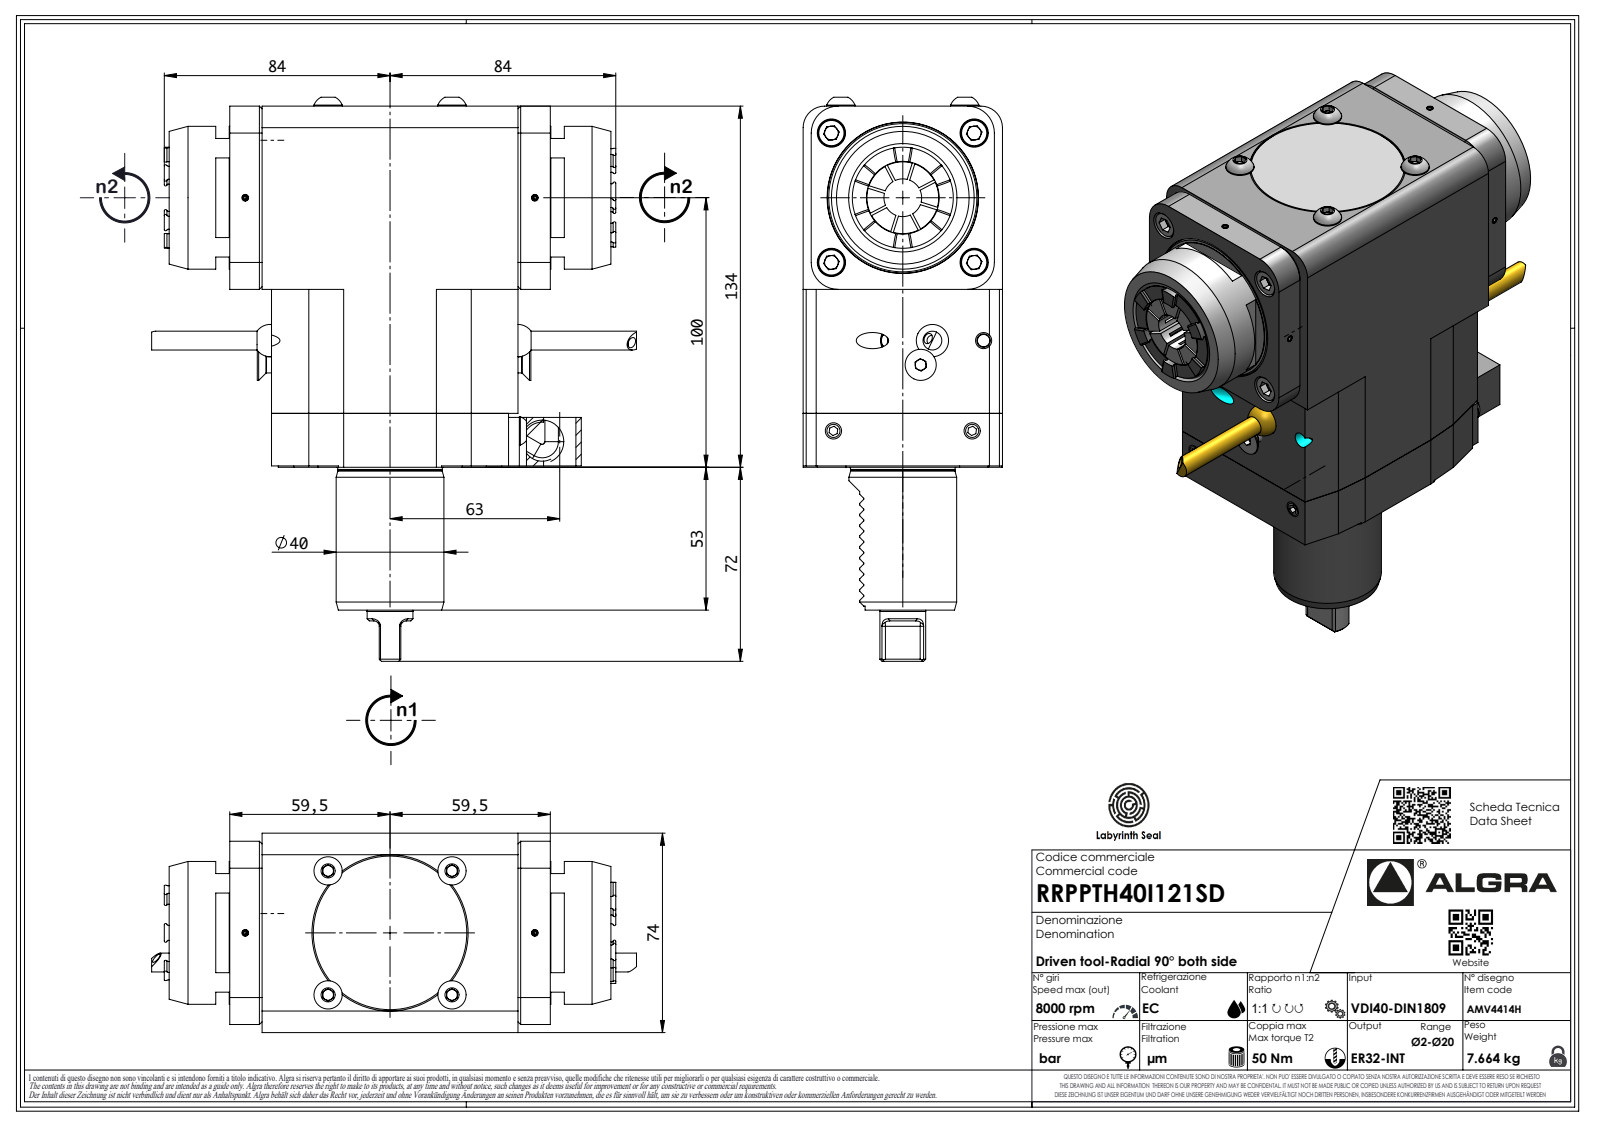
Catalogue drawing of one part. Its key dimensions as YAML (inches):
part_name: "RRPPTH40I121SD"
step_written_by: "SolidWorks 2023 (AUTOMOTIVE_DESIGN)"
units: inches
bodies: {solids: 1, faces: 472, planar: 331, cylindrical: 62, other: 79}
overall_size: [8.11, 6.457, 2.913]
volume: 72.68
surface_area: 127.5
round_holes:
  - {diameter: 0.083, count: 1}
round_bosses_or_shafts:
  - {diameter: 2.087, count: 1}
  - {diameter: 1.575, count: 1}
  - {diameter: 1.524, count: 1}
  - {diameter: 0.669, count: 1}
  - {diameter: 0.669, count: 1}
  - {diameter: 0.251, count: 1}
  - {diameter: 0.067, count: 1}
partial_cylinders:
  - {radius: 0.012, count: 11}
  - {radius: 0.013, count: 7}
  - {radius: 0.02, count: 7}
  - {radius: 0.146, count: 7}
  - {radius: 0.079, count: 6}
  - {radius: 0.394, count: 4}
  - {radius: 0.315, count: 2}
  - {radius: 0.008, count: 1}
face_to_face_distances: [2.913, 0.472, 0.886, 5.571, 5.276, 4.685, 3.602, 2.677, 4.213, 4.075]
